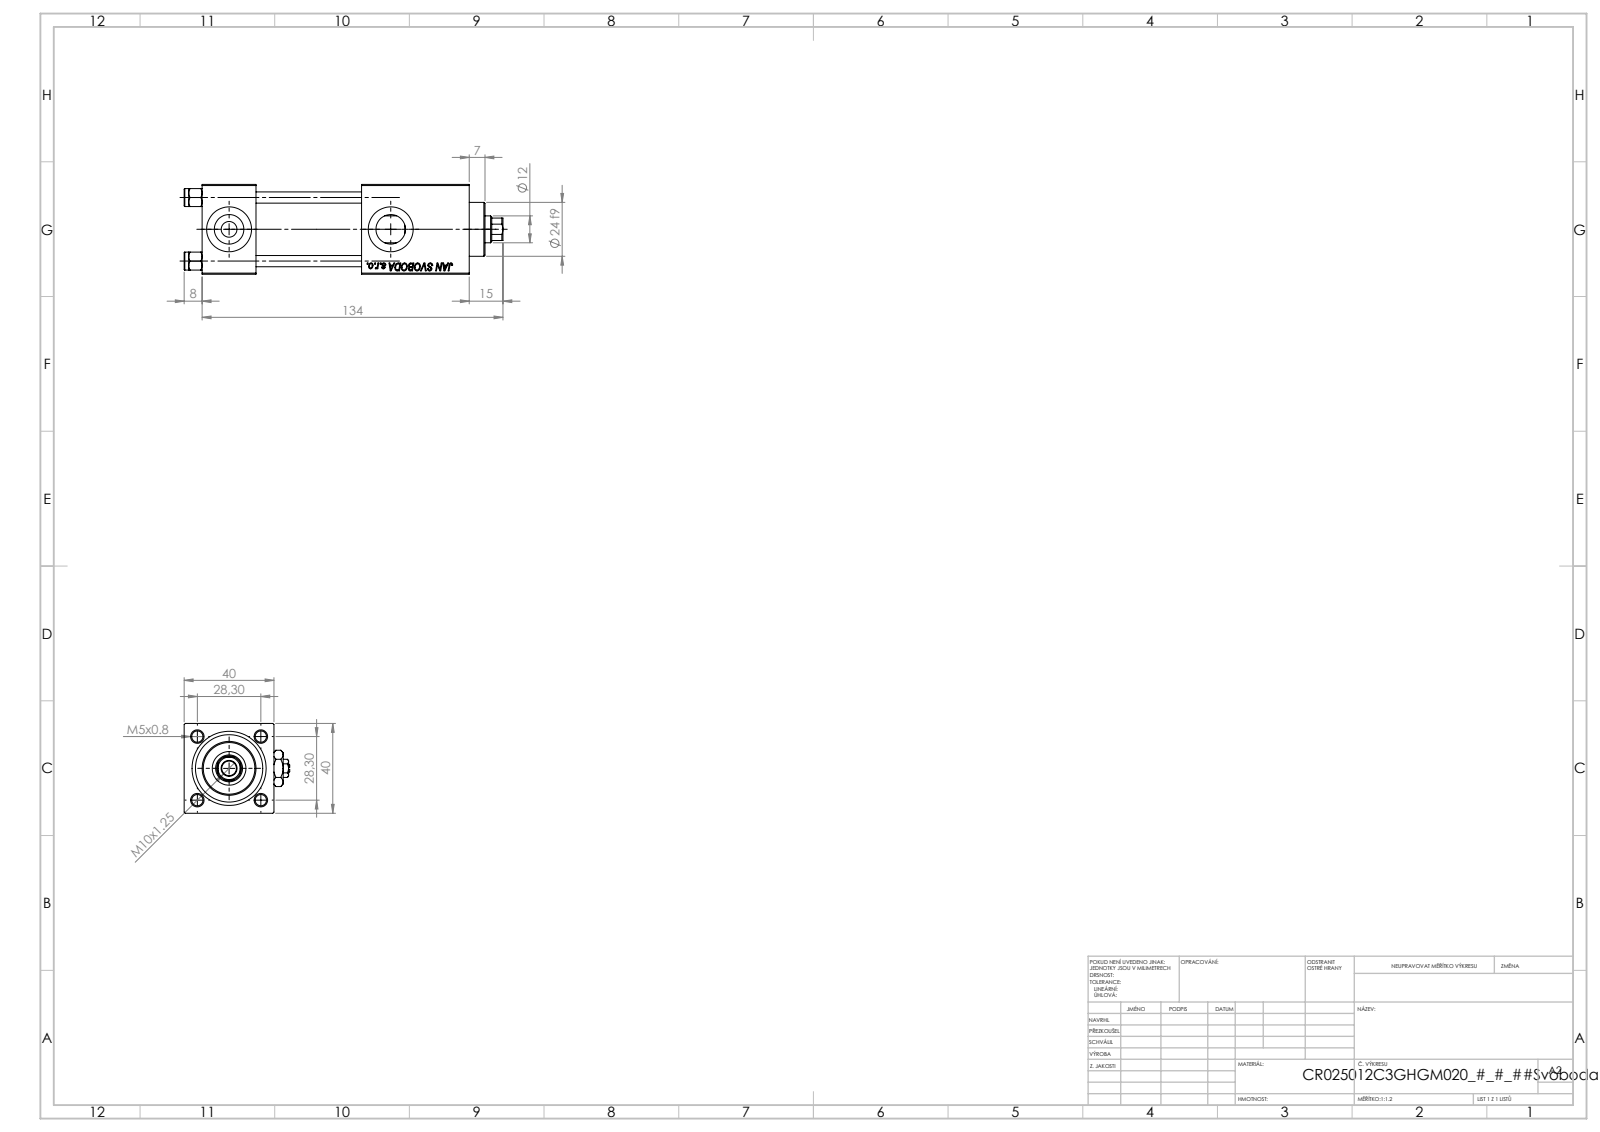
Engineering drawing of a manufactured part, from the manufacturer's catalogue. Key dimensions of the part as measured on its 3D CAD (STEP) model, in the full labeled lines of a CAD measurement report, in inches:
Part name (STEP PRODUCT): V215CR_C_Body; V215_VC_A; Zatka_pro_OIL_PORT; NUT_M5_C (+2 more)
STEP written by: SolidWorks 2019 (CONFIG_CONTROL_DESIGN)
Units: inches
Bodies: 13 solids, 1248 faces (572 planar, 98 cylindrical, 578 other)
Overall size (bounding box): 5.591 × 1.85 × 1.575
Volume: 8.603 in³ · Surface area: 87.12 in²
Round holes (diameter × count): ⌀0.197 ×4, ⌀0.787 ×3, ⌀0.276 ×2, ⌀0.518 ×2, ⌀0.256 ×1, ⌀0.472 ×1, ⌀0.591 ×1, ⌀0.984 ×1, ⌀1.181 ×1
Round bosses / shafts (diameter × count): ⌀0.315 ×4, ⌀1.22 ×1, ⌀0.945 ×1
Partial cylindrical surfaces — rounded edges, fillets, slot ends (radius × count): R0.217 ×1
Main face-to-face distances: 1.575, 0.945, 1.567, 3.555, 2.61, 1.89, 1.85, 2.795, 0.76, 4.685
Hole centre spacings: 0.788, 1.114, 1.576, 2.835
